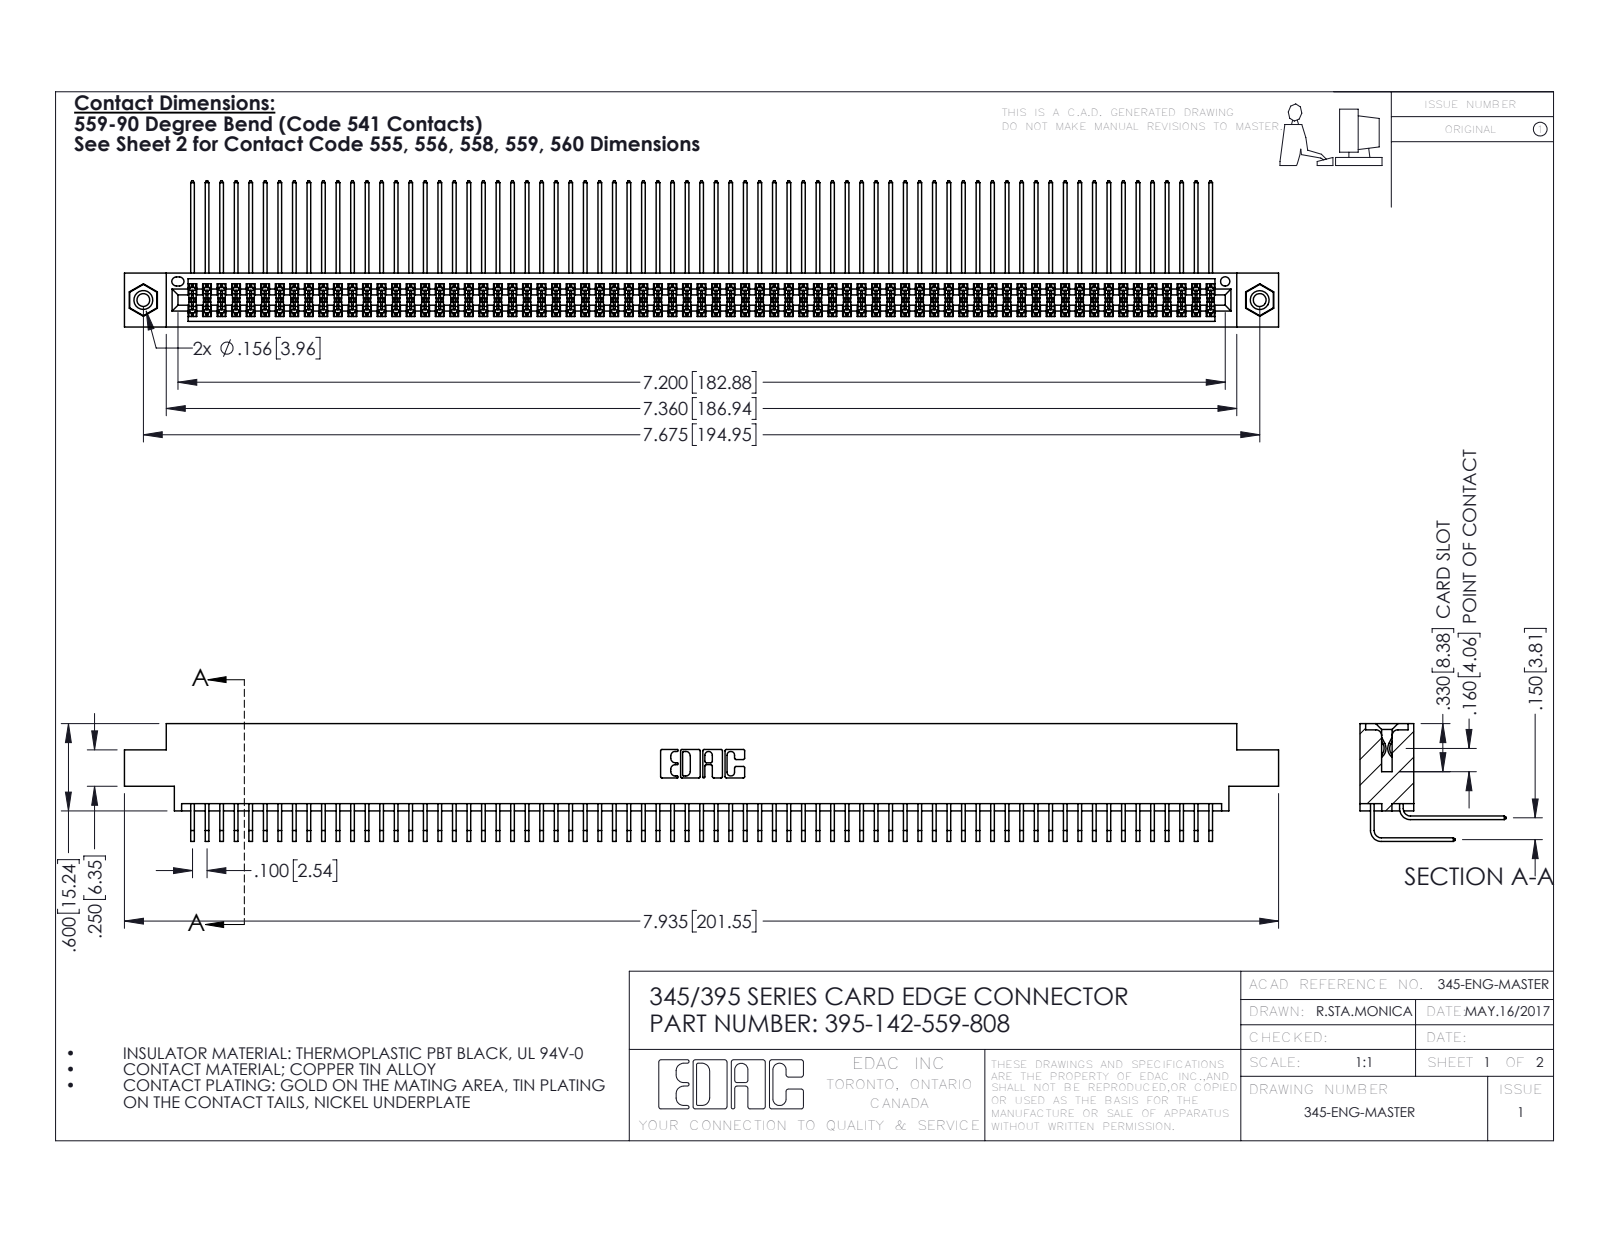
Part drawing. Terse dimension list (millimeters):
name: 345-292-001_559 Tail - 2; 345-250-001_345-250-003-102; 395-142-559-808; 345-292-001_558 559 Tail - 1 (+1 more)
written by: SolidWorks 2016 (CONFIG_CONTROL_DESIGN)
unit: mm
bodies: 145 solids, 7574 faces (5086 planar, 2472 cylindrical, 16 other)
size: 201.5 × 25.5 × 20.5
volume: 20 550 mm³; area: 34 940 mm²
holes: 2× ⌀2.3, 2× ⌀3.2, 2× ⌀4, 1× ⌀1.6
bosses: 2× ⌀3.9
rounds: 284× R0.2, 22× R0.3, 6× R0.2, 6× R0.8, 3× R0.7, 2× R0.4, 2× R0.5, 2× R0.6
face distances: 1.8, 7.6, 5.1, 9.4, 2.5, 6.9, 0.6, 5.7, 4.4, 3.8
hole spacings: 6.9, 189, 194.9
